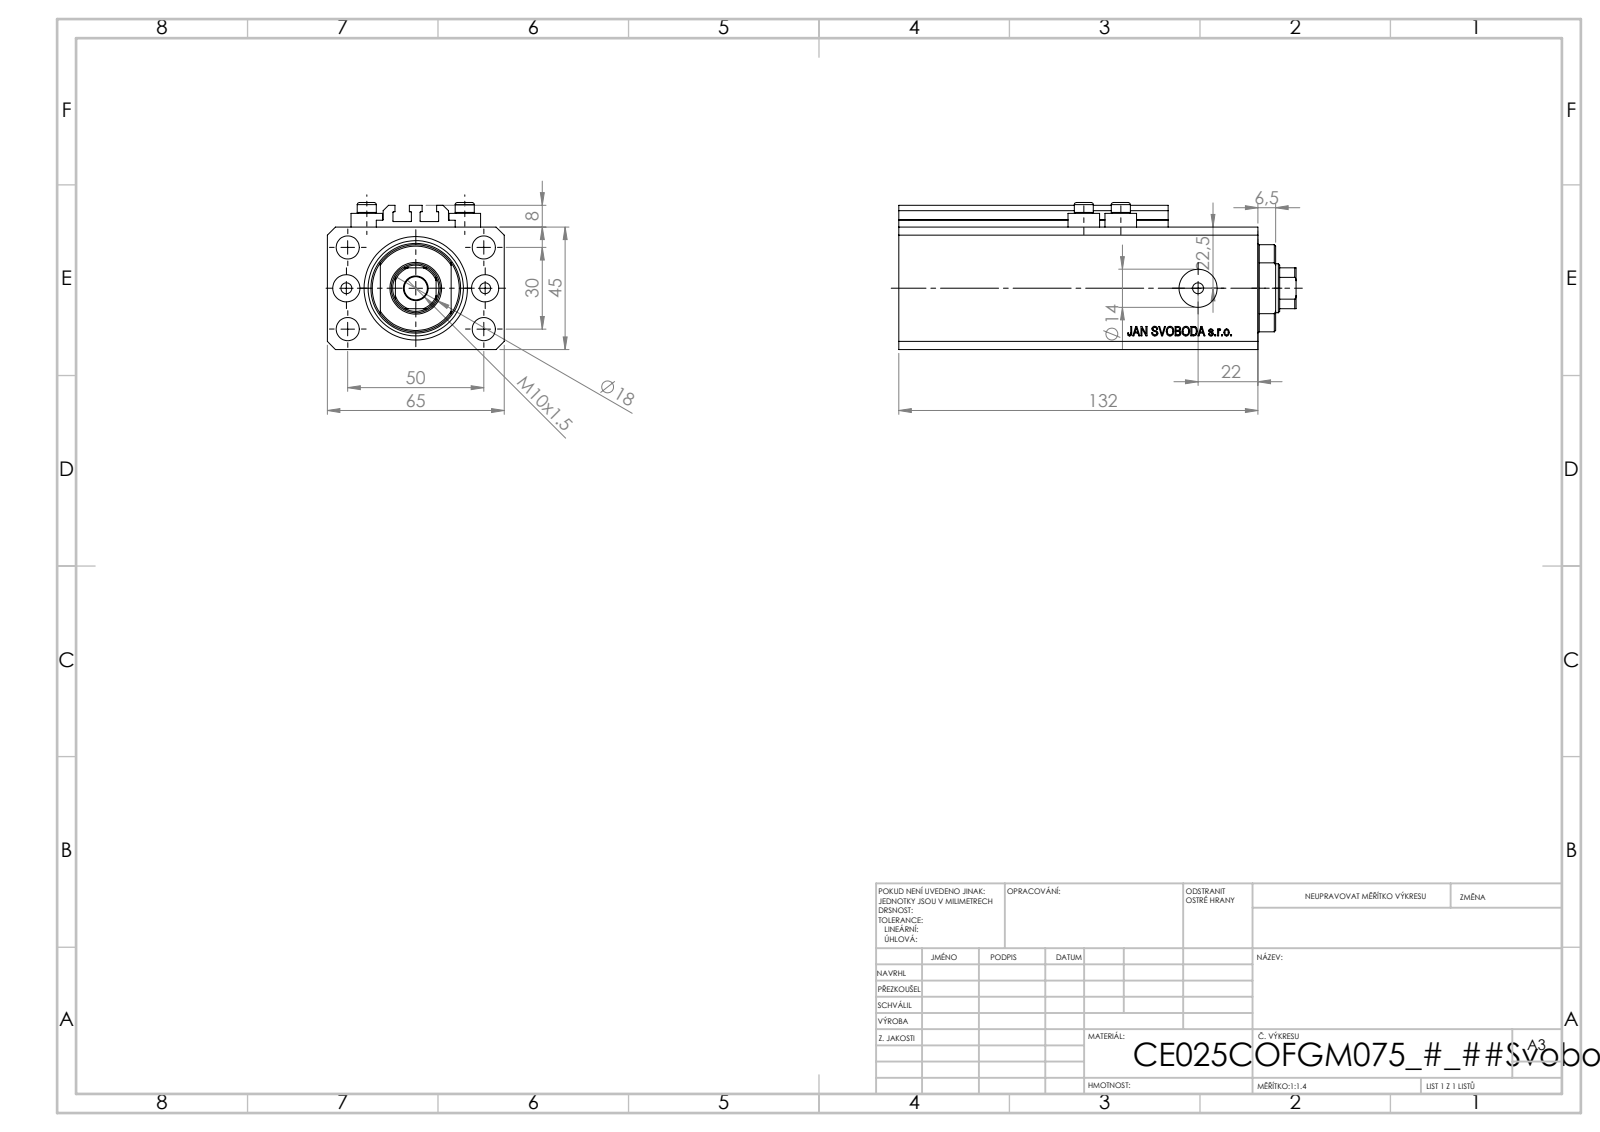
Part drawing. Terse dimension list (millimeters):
name: ALLEN BOLT V250CE; V250CE_C_VCP; V250CE_C_Body; V250CE_VC_C
written by: SolidWorks 2019 (CONFIG_CONTROL_DESIGN)
unit: mm
bodies: 8 solids, 1034 faces (504 planar, 86 cylindrical, 444 other)
size: 146 × 65 × 54
volume: 353 278 mm³; area: 87 828 mm²
holes: 8× ⌀4, 5× ⌀8.5, 2× ⌀10, 2× ⌀14, 1× ⌀18, 1× ⌀25, 1× ⌀38
bosses: 4× ⌀11.6, 4× ⌀7
rounds: 10× R0.2, 1× R8.5, 1× R16
face distances: 45, 65, 47, 14, 118, 132, 2.5, 2, 10, 20.5
hole spacings: 15.01, 29.15, 52.68, 13.6, 25.5, 30, 36, 38.48
